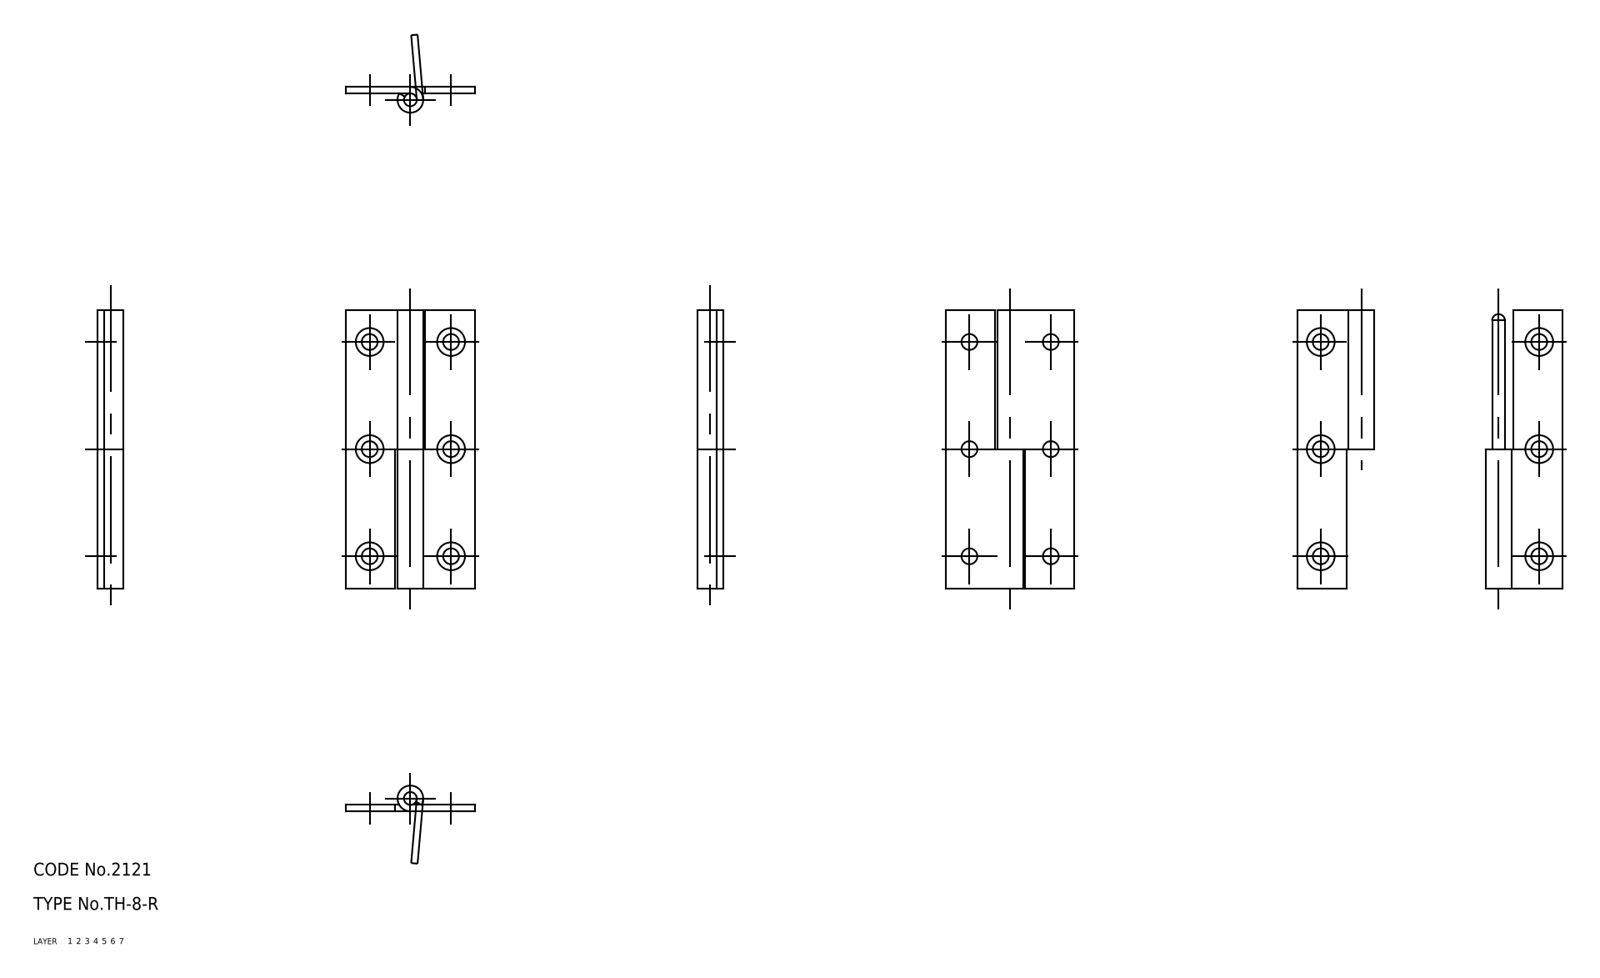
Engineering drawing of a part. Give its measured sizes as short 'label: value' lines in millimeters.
name: shaft; hinge piece_B; hinge piece_A; TH_8_R_18365_36
written by: CADfix (AUTOMOTIVE_DESIGN)
unit: mm
bodies: 3 solids, 48 faces (0 planar, 0 cylindrical, 48 other)
size: 65 × 30 × 6
volume: 3 996 mm³; area: 6 066 mm²
